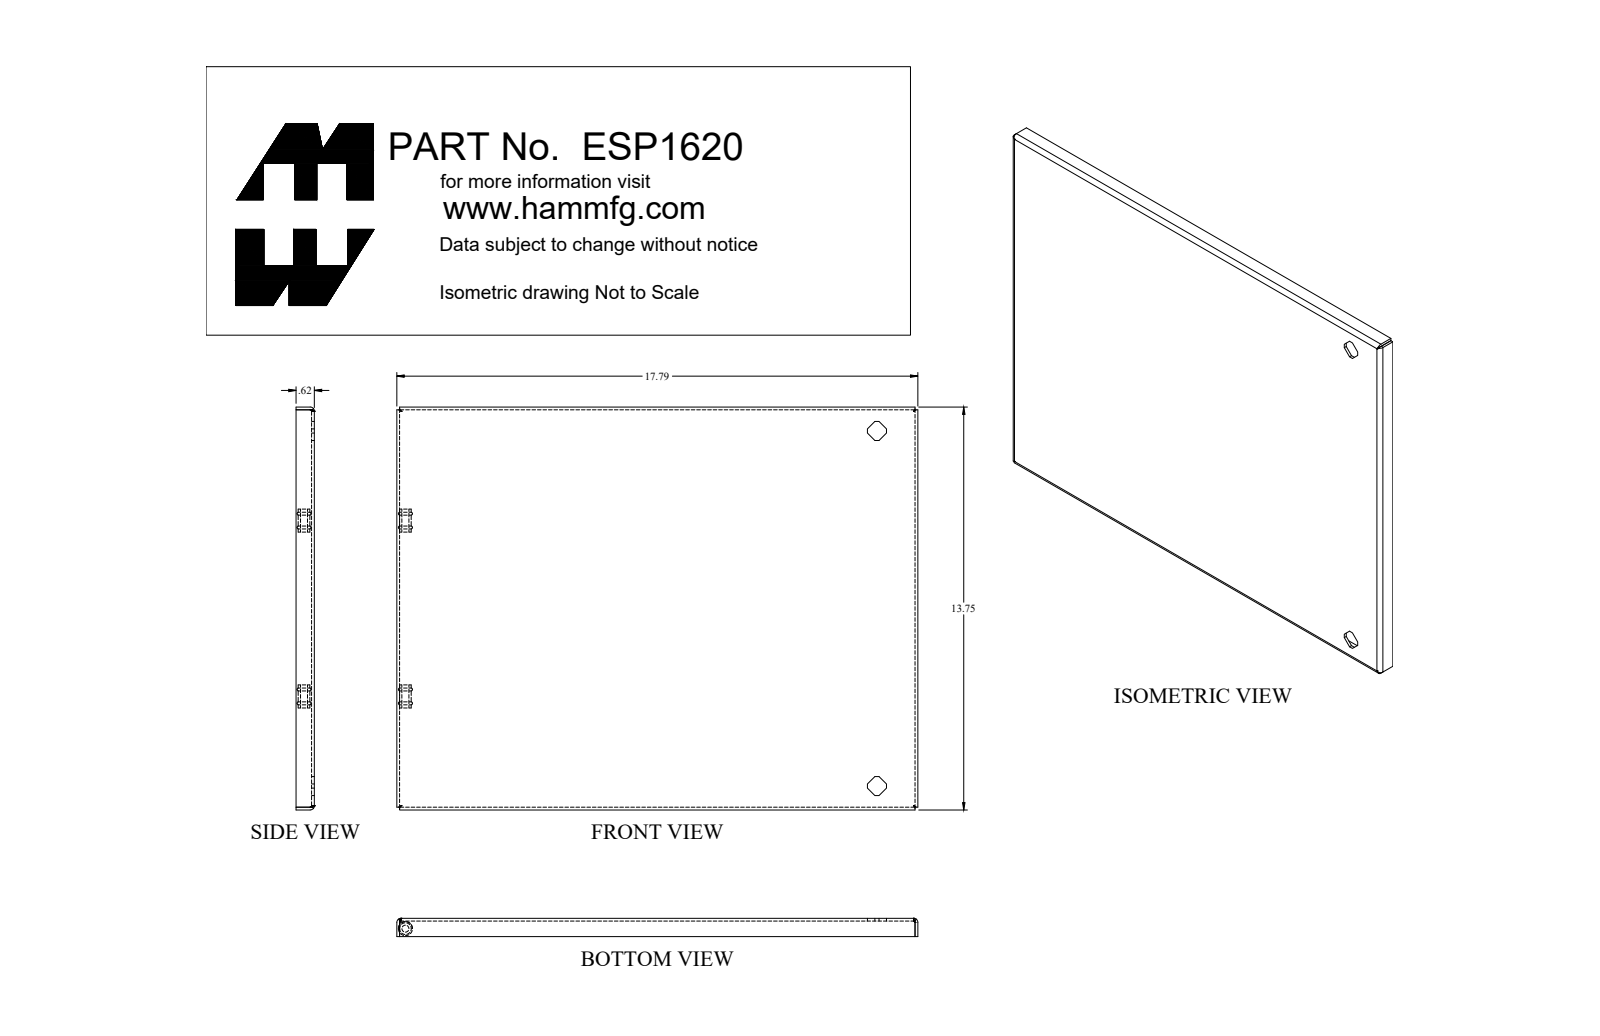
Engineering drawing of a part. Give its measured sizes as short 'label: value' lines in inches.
name: ESP1620
written by: SolidWorks 2018 (AUTOMOTIVE_DESIGN)
unit: in
bodies: 13 solids, 584 faces (354 planar, 174 cylindrical, 56 other)
size: 19.706 × 13.75 × 9.953
volume: 37.27 in³; area: 969 in²
holes: 2× ⌀0.136, 2× ⌀0.242, 2× ⌀0.516
bosses: 6× ⌀0.232, 2× ⌀0.788, 2× ⌀0.535, 2× ⌀0.496, 2× ⌀0.435, 2× ⌀0.356
rounds: 28× R0.048, 24× R0.01, 6× R0.036, 6× R0.108, 4× R0.06, 4× R0.143, 4× R0.153, 4× R0.156
face distances: 0.095, 0.072, 0.038, 0.813, 0.775, 0.775, 18.008, 12.062, 18.893, 0.038
hole spacings: 6, 12.159
